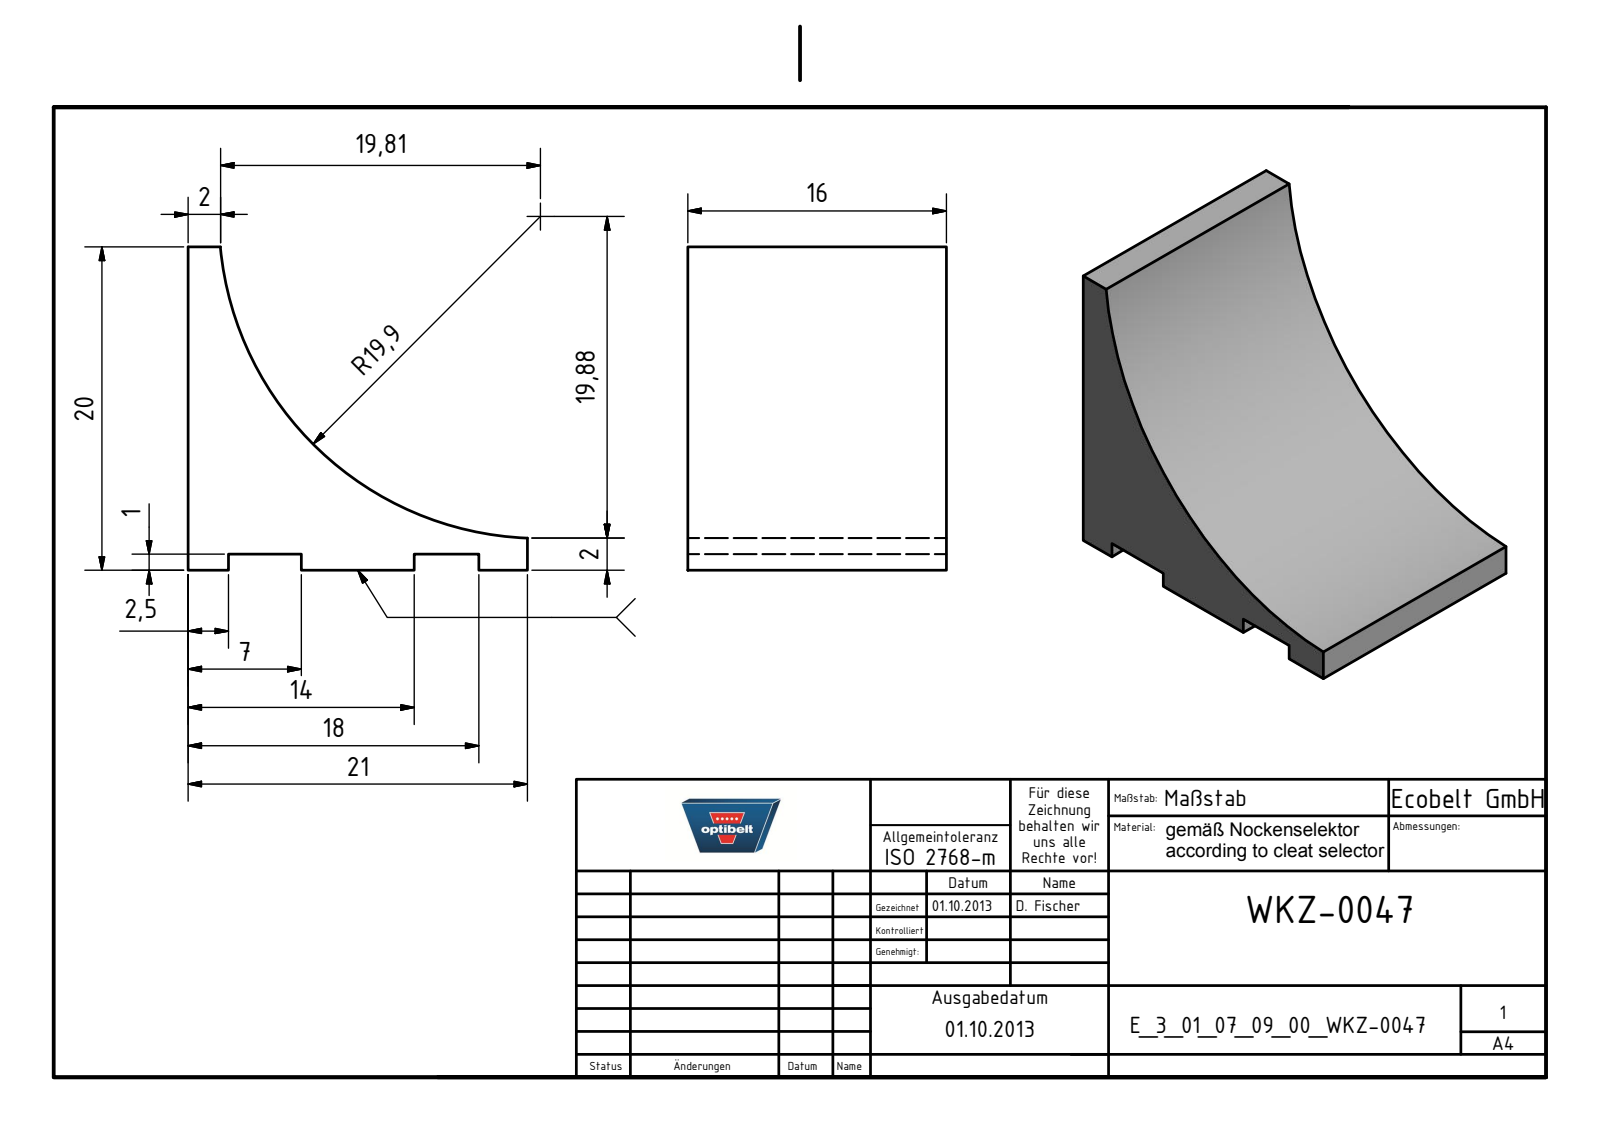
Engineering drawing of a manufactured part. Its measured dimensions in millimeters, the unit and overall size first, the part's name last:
Units: millimetres
Overall size (bounding box): 21 × 20 × 16
Partial cylindrical surfaces — rounded edges, fillets, slot ends (radius × count): R19.9 ×1
Main face-to-face distances: 16, 1, 7, 14, 21, 20, 19, 2.5, 4.5, 18.5
Volume: 2 440 mm³ · Surface area: 1 546 mm²
Bodies: 1 solid, 15 faces (14 planar, 1 cylindrical, 0 other)
Part name (STEP PRODUCT): E_3_01_07_09_00_WKZ-0047
STEP written by: Autodesk Inventor 2025 (AUTOMOTIVE_DESIGN)
